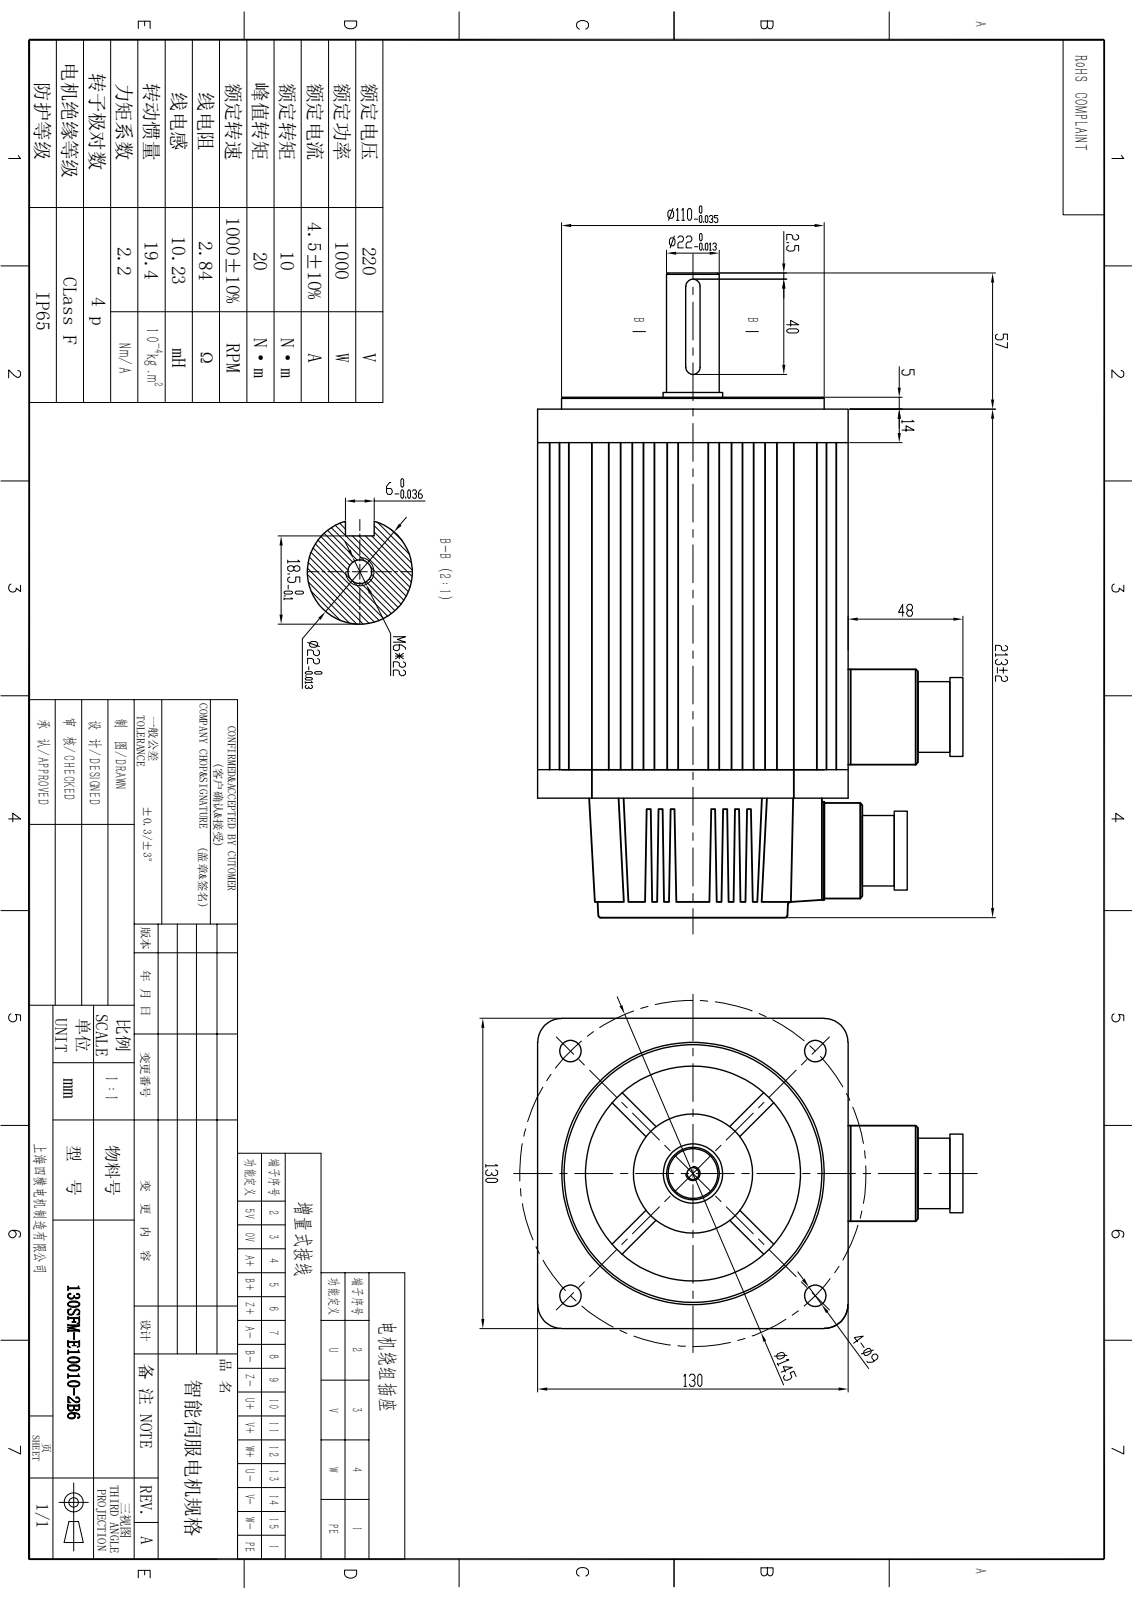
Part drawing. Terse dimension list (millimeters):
name: 130SFM-E10010-2B6
written by: SolidWorks 2020 (CONFIG_CONTROL_DESIGN)
unit: mm
bodies: 10 solids, 1040 faces (395 planar, 277 cylindrical, 368 other)
size: 270 × 172 × 130
volume: 2 841 000 mm³; area: 261 729 mm²
holes: 8× ⌀2.5, 4× ⌀6.5, 4× ⌀9, 4× ⌀11, 2× ⌀25, 1× ⌀5, 1× ⌀99
bosses: 15× ⌀1.5, 4× ⌀10, 4× ⌀6, 3× ⌀4, 2× ⌀30, 1× ⌀110, 1× ⌀80, 1× ⌀70
rounds: 76× R0.5, 10× R3, 8× R2, 4× R10, 1× R49.75, 1× R64.5
face distances: 134, 12, 146, 130, 2, 128, 160, 14, 148, 21
hole spacings: 19.8, 26.87, 28, 38, 68, 96.17, 102.53, 16.56
